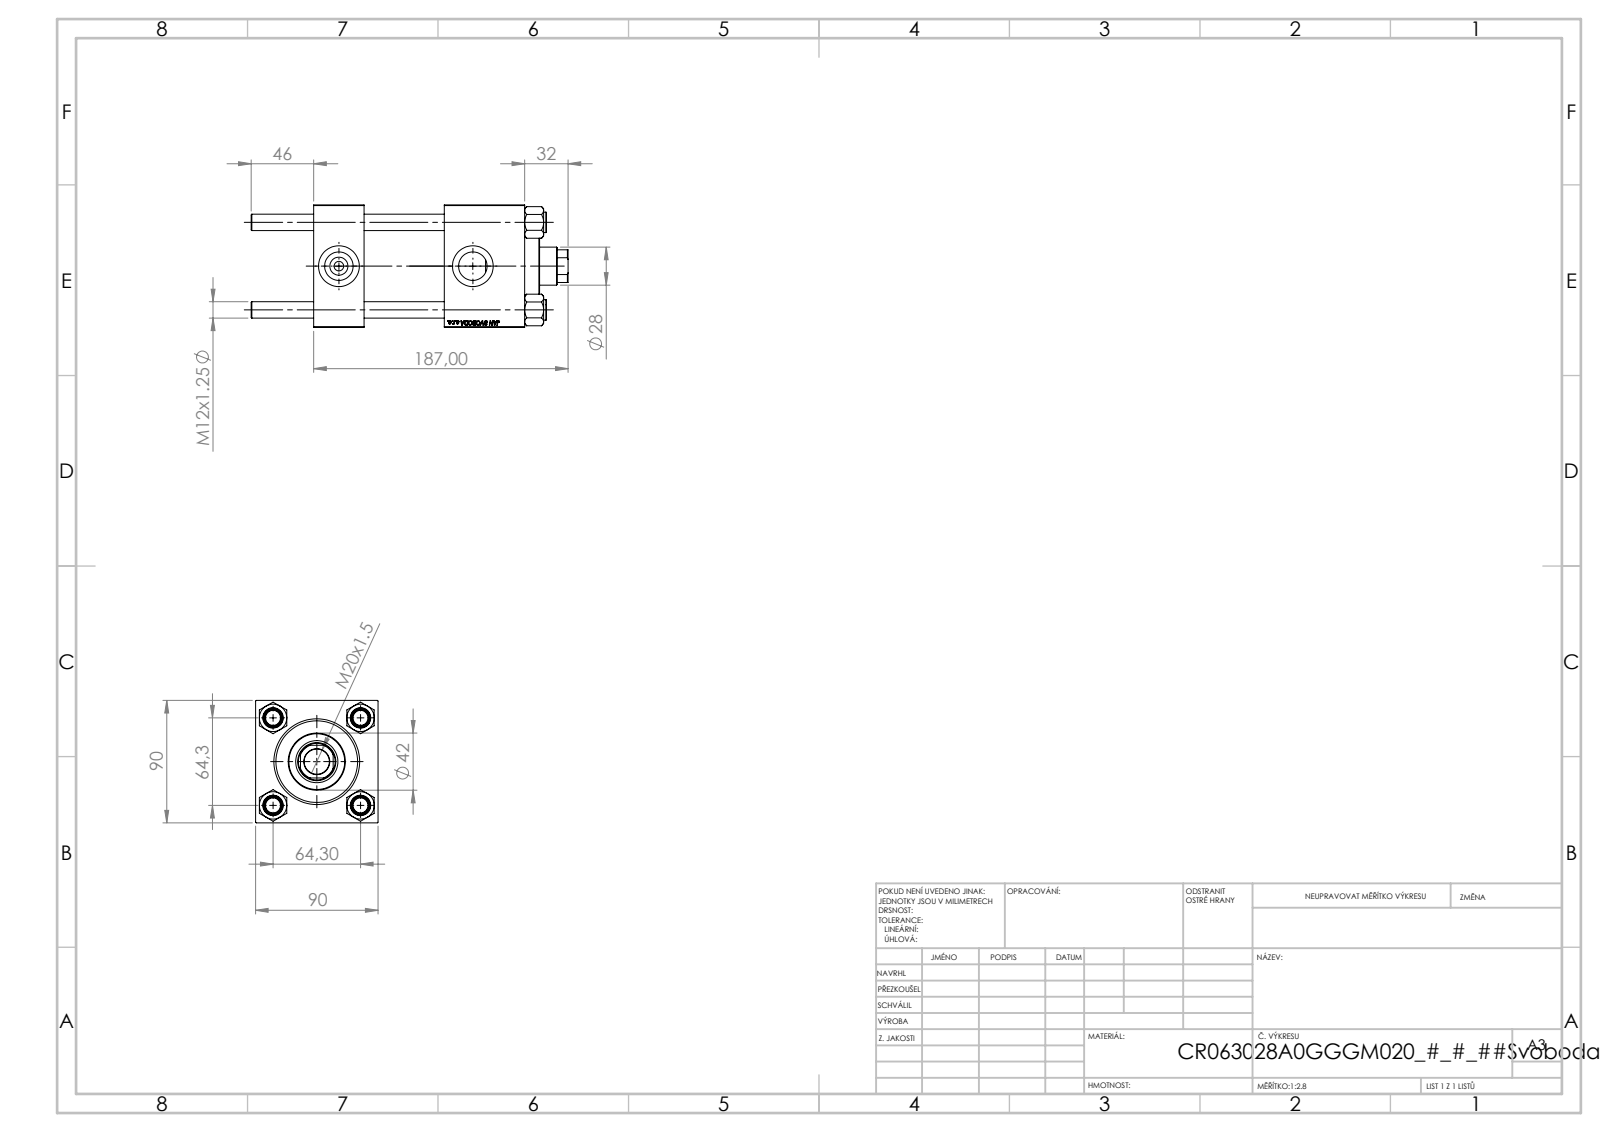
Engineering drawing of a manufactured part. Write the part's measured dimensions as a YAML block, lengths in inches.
part_name: "CR025_012_A_0_G_A_G_M_020_+#_##_TYCINKA; V215_VC_A; V215CR_BODY_A; NUT_M5 (+1 more)"
step_written_by: "SolidWorks 2019 (CONFIG_CONTROL_DESIGN)"
units: inches
bodies: {solids: 11, faces: 1134, planar: 519, cylindrical: 79, other: 536}
overall_size: [9.173, 3.543, 3.543]
volume: 59.79
surface_area: 303.4
round_holes:
  - {diameter: 0.472, count: 4}
  - {diameter: 0.276, count: 2}
  - {diameter: 0.825, count: 2}
  - {diameter: 1.181, count: 2}
  - {diameter: 0.728, count: 1}
  - {diameter: 1.102, count: 1}
  - {diameter: 1.22, count: 1}
  - {diameter: 1.969, count: 1}
  - {diameter: 2.362, count: 1}
  - {diameter: 2.48, count: 1}
round_bosses_or_shafts:
  - {diameter: 0.591, count: 4}
  - {diameter: 2.717, count: 1}
  - {diameter: 1.654, count: 1}
partial_cylinders:
  - {radius: 0.531, count: 1}
face_to_face_distances: [3.543, 2.323, 1.457, 6.102, 4.646, 3.78, 4.972, 3.516, 1.193, 1.13]
hole_center_spacings: [1.79, 2.531, 3.58, 3.876]
